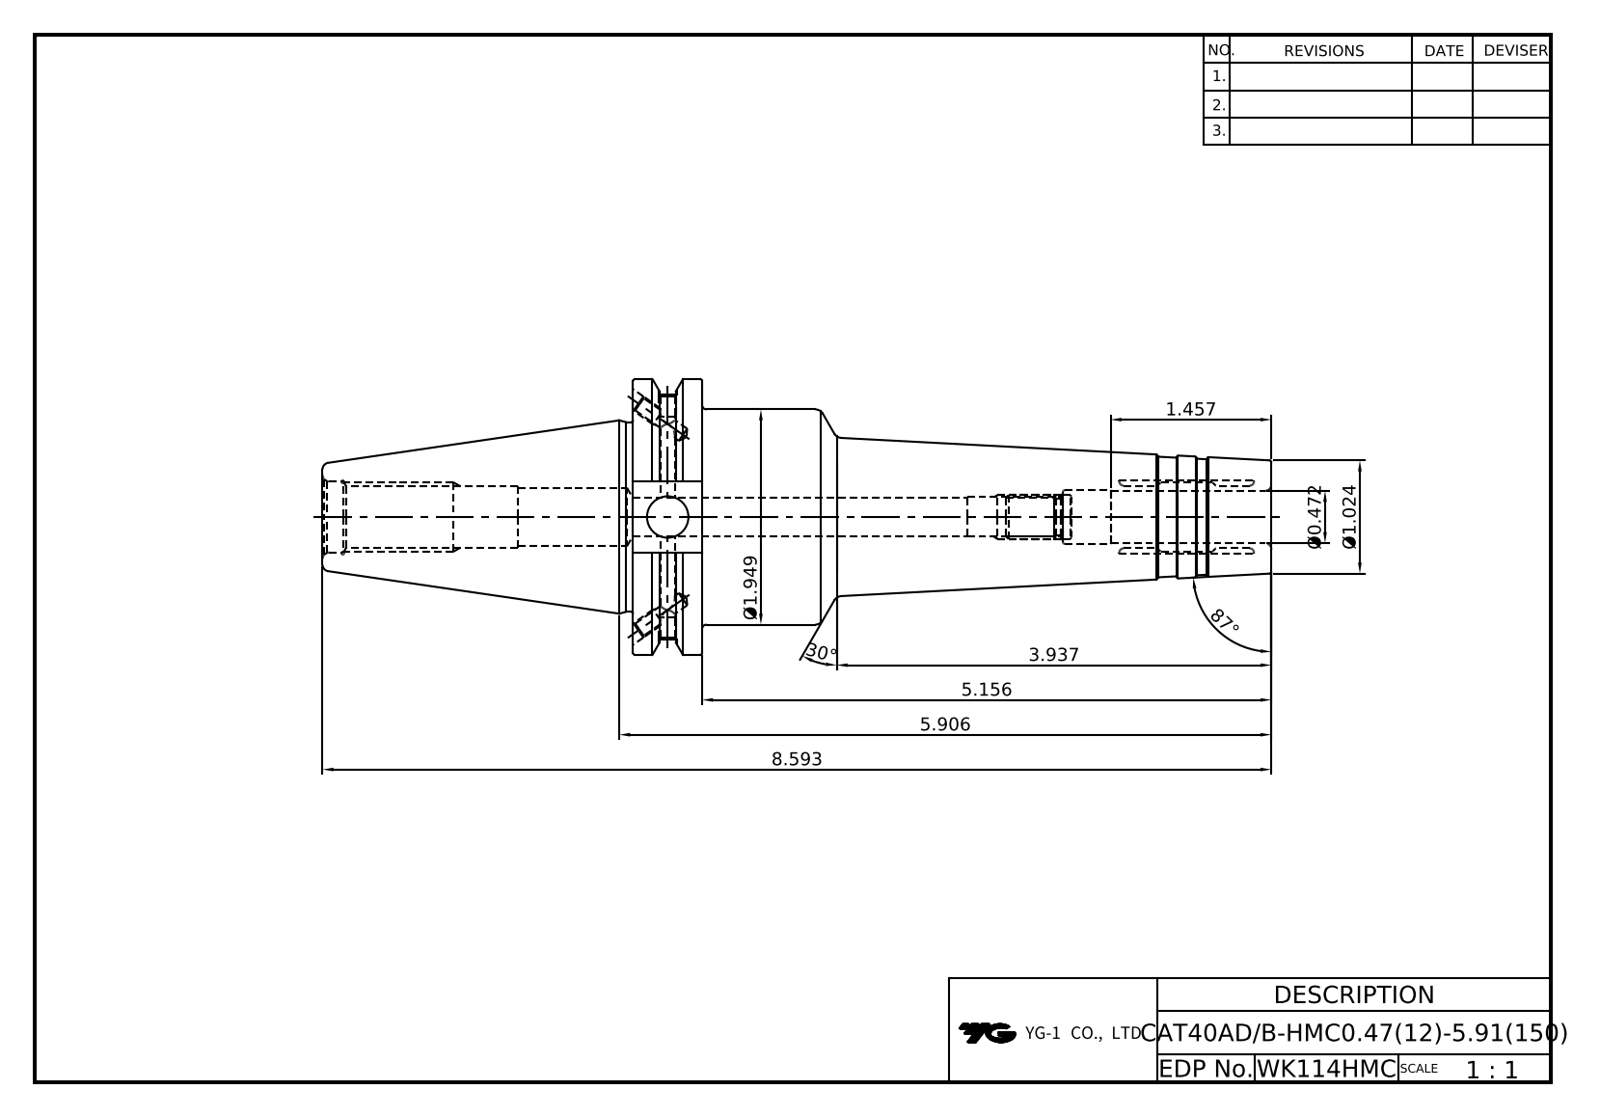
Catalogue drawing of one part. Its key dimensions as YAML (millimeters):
part_name: "LO-CAT40ADB-HMC12-150"
step_written_by: "Autodesk Inventor 2020 (AUTOMOTIVE_DESIGN)"
units: millimeters
bodies: {solids: 1, faces: 106, planar: 36, cylindrical: 30, other: 40}
overall_size: [218.25, 63.5, 61.09]
volume: 220892
surface_area: 38080
round_holes:
  - {diameter: 3.24, count: 4}
  - {diameter: 4, count: 2}
  - {diameter: 4.2, count: 2}
  - {diameter: 8.92, count: 1}
  - {diameter: 9.53, count: 1}
  - {diameter: 12, count: 1}
  - {diameter: 12.6, count: 1}
  - {diameter: 13, count: 1}
  - {diameter: 13.39, count: 1}
  - {diameter: 16.3, count: 1}
round_bosses_or_shafts:
  - {diameter: 63.5, count: 1}
  - {diameter: 49.5, count: 1}
  - {diameter: 43.6, count: 1}
partial_cylinders:
  - {radius: 8.19, count: 1}
  - {radius: 28.15, count: 1}
face_to_face_distances: [15.88, 146.83, 130.95, 47.6, 16.38, 71.42, 87.3, 218.25, 77.47, 6.05]
